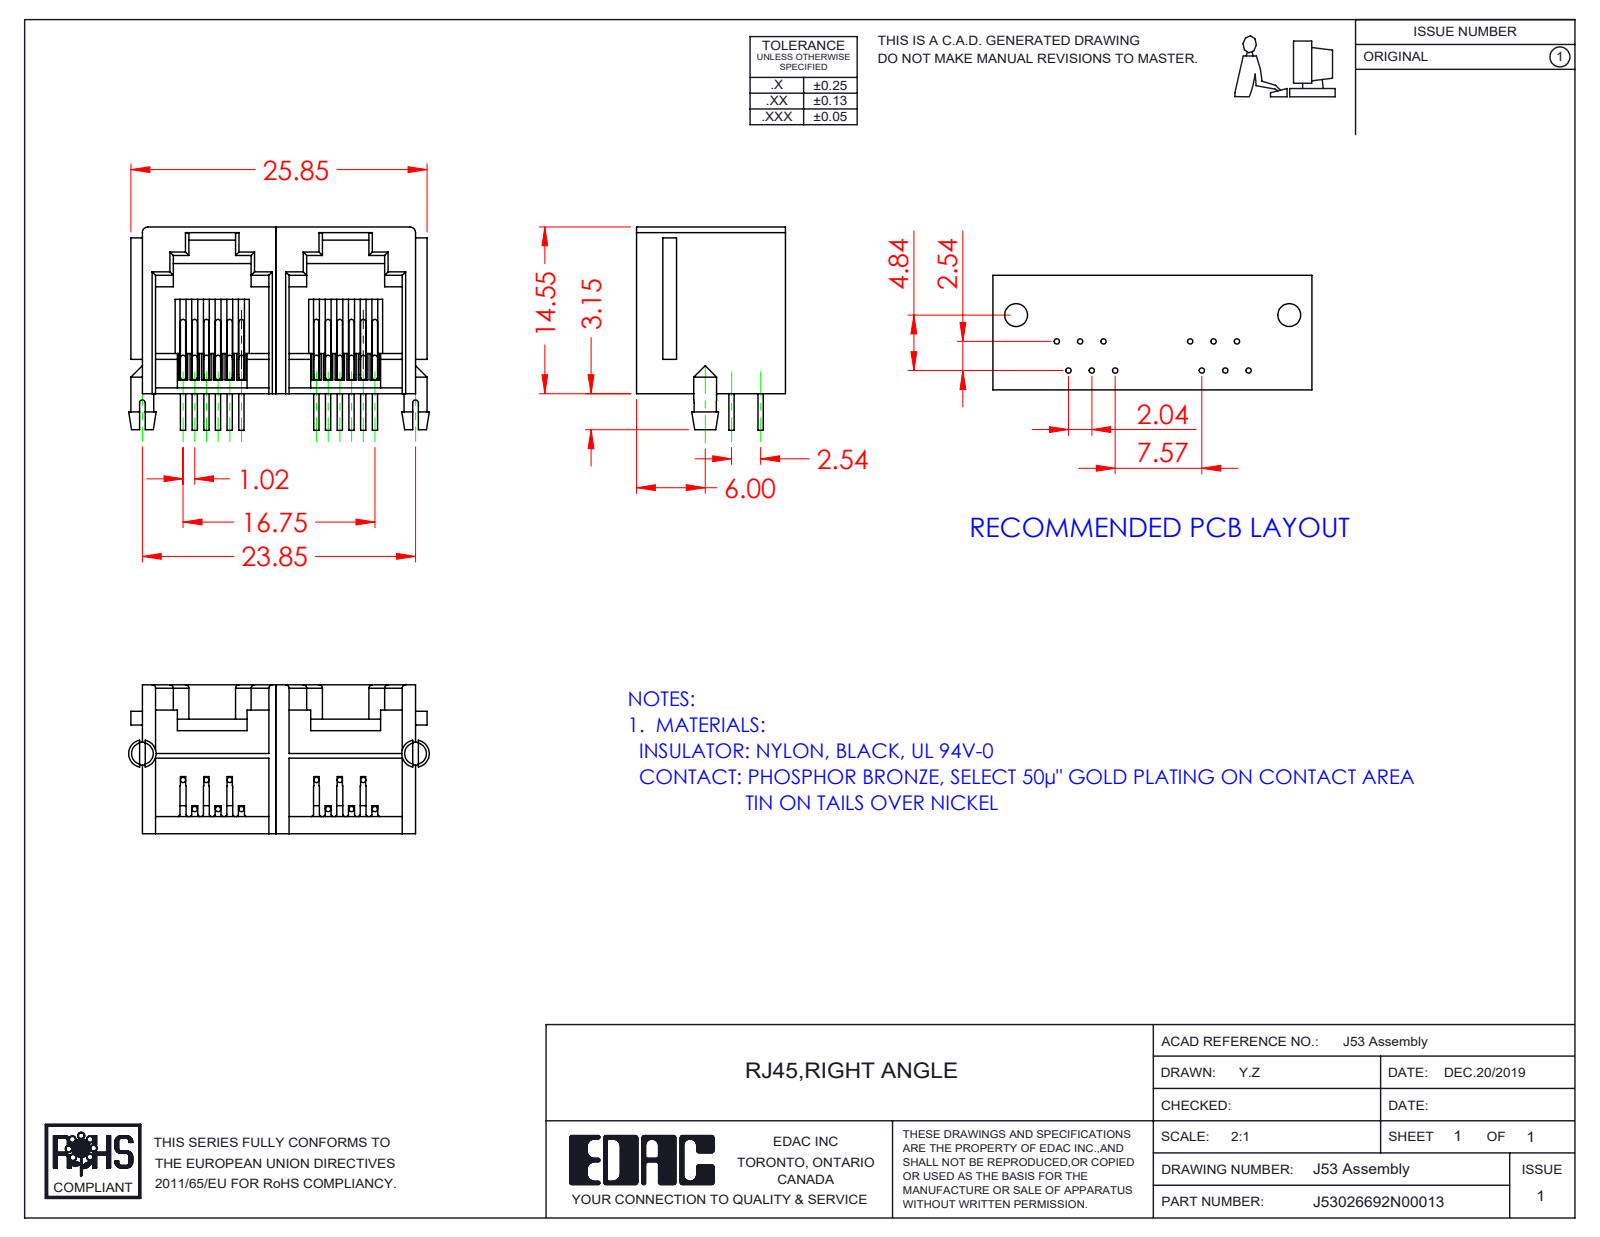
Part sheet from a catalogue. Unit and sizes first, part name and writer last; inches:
Units: inches
Overall size (bounding box): 1.033 × 0.699 × 0.512
Round bosses / shafts (diameter × count): ⌀0.018 ×36, ⌀0.079 ×2
Partial cylindrical surfaces — rounded edges, fillets, slot ends (radius × count): R0.012 ×14, R0.02 ×10, R0.01 ×2, R0.026 ×1
Main face-to-face distances: 0.459, 0.046, 0.435, 0.48, 0.893, 0.413, 0.504, 0.024, 0.389, 0.118
Volume: 0.11 in³ · Surface area: 6.634 in²
Bodies: 14 solids, 595 faces (410 planar, 128 cylindrical, 57 other)
Part name (STEP PRODUCT): 53 Contact - 3; 53 Insulator LH; 53 Contact - 5; 53 Contact - 4 (+6 more)
STEP written by: SolidWorks 2016 (CONFIG_CONTROL_DESIGN)
